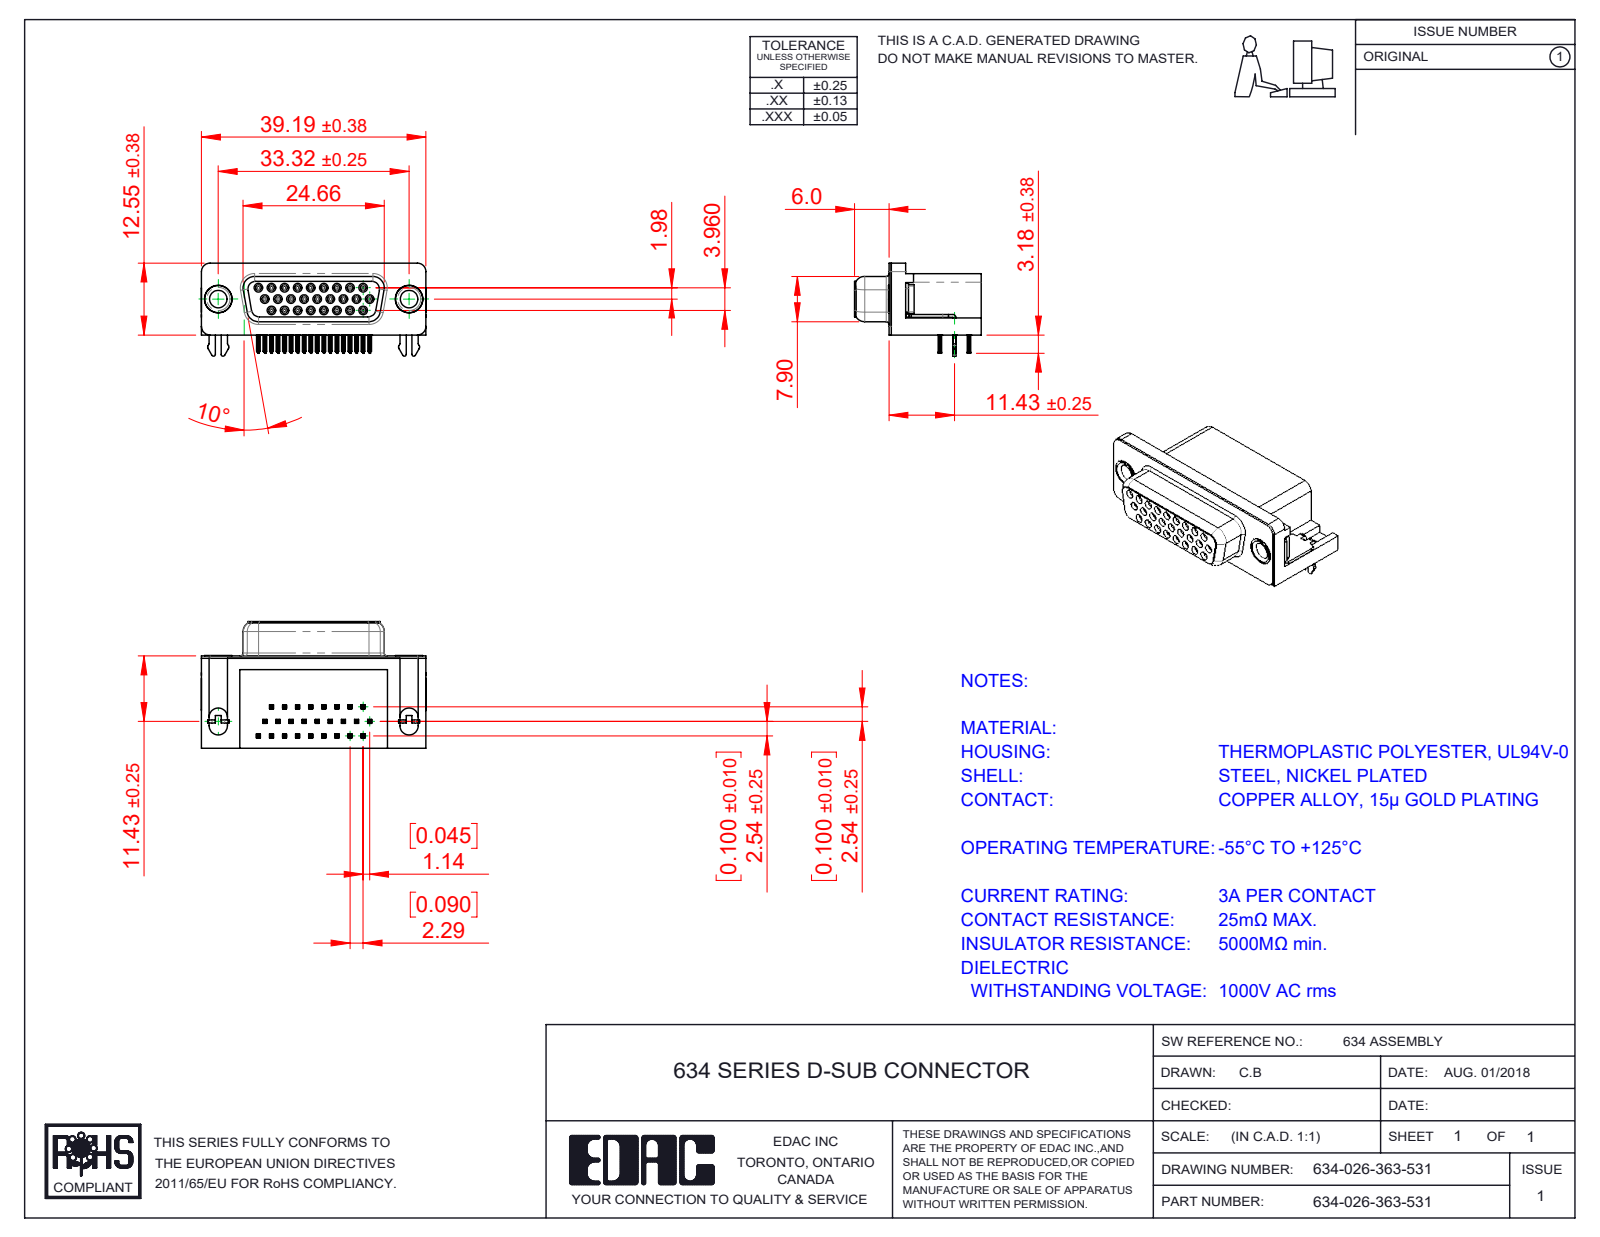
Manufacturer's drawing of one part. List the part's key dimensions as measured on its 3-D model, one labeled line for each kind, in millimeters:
Part name (STEP PRODUCT): 634 Housing_26 Socket; Contact Bottom; 634 Shell_26 Socket; 2 Prong Board Lock (+4 more)
STEP written by: SolidWorks 2016 (CONFIG_CONTROL_DESIGN)
Units: millimetres
Bodies: 32 solids, 3981 faces (1803 planar, 928 cylindrical, 1250 other)
Overall size (bounding box): 39.22 × 22.1 × 16.25
Volume: 6 354 mm³ · Surface area: 9 065 mm²
Round holes (diameter × count): ⌀0.8 ×26, ⌀0.9 ×26, ⌀3.05 ×2, ⌀4 ×2, ⌀4.8 ×2, ⌀5 ×2
Round bosses / shafts (diameter × count): ⌀1.2 ×26, ⌀4.9 ×2, ⌀4.75 ×2, ⌀3.85 ×2
Partial cylindrical surfaces — rounded edges, fillets, slot ends (radius × count): R0.1 ×208, R0.15 ×104, R0.35 ×52, R0.34 ×26, R1 ×19, R0.5 ×10, R0.25 ×8, R0.28 ×8
Main face-to-face distances: 0.4, 10.34, 0.35, 15.7, 16.1, 6.65, 2.5, 0.85, 2.9, 10.69
Hole centre spacings: 2.29, 4.57, 2.28, 3.96, 6.05, 2.3, 2.27, 4.58
